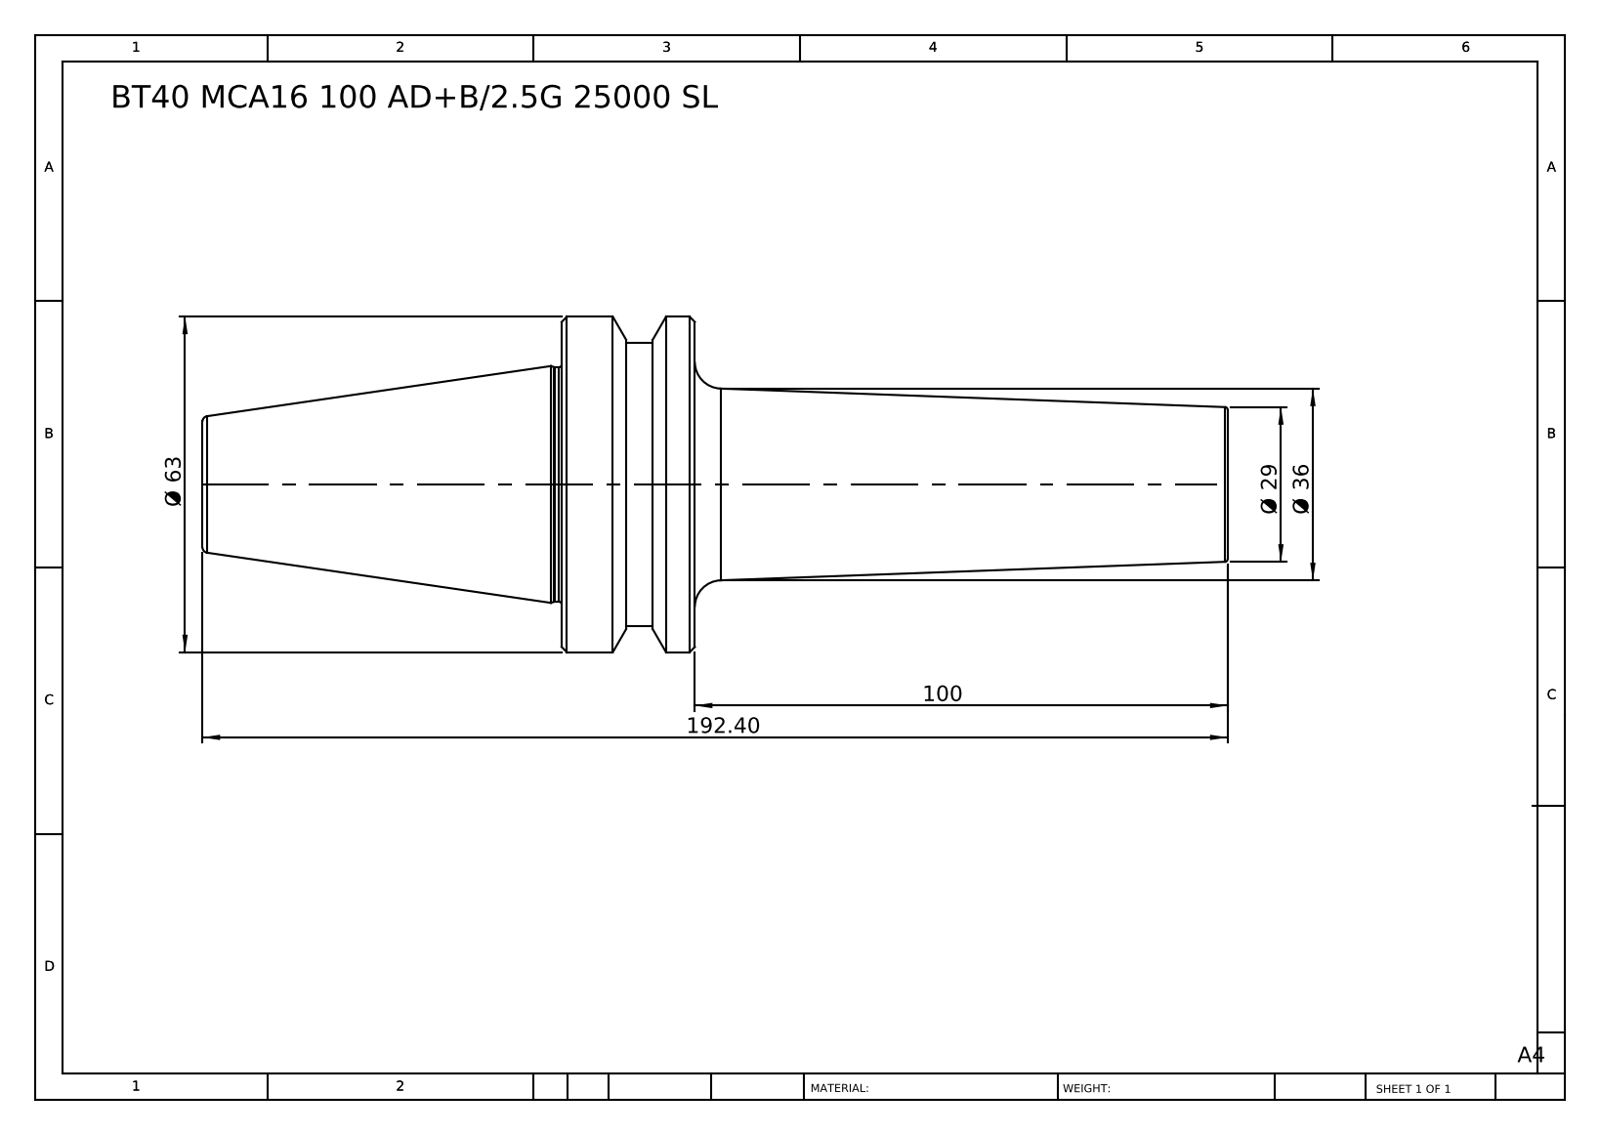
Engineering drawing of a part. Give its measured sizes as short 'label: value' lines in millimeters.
name: BT40 MCA16 100 AD+B-2.5G 25000 SL
written by: SolidWorks 2014 (CONFIG_CONTROL_DESIGN)
unit: mm
bodies: 1 solid, 38 faces (6 planar, 8 cylindrical, 24 other)
size: 192.4 × 63 × 63
volume: 223 155 mm³; area: 27 996 mm²
bosses: 1× ⌀63, 1× ⌀53, 1× ⌀44
face distances: 25, 100, 125, 192.4, 92.4, 67.4, 112.9, 12.9, 12.1, 79.5
